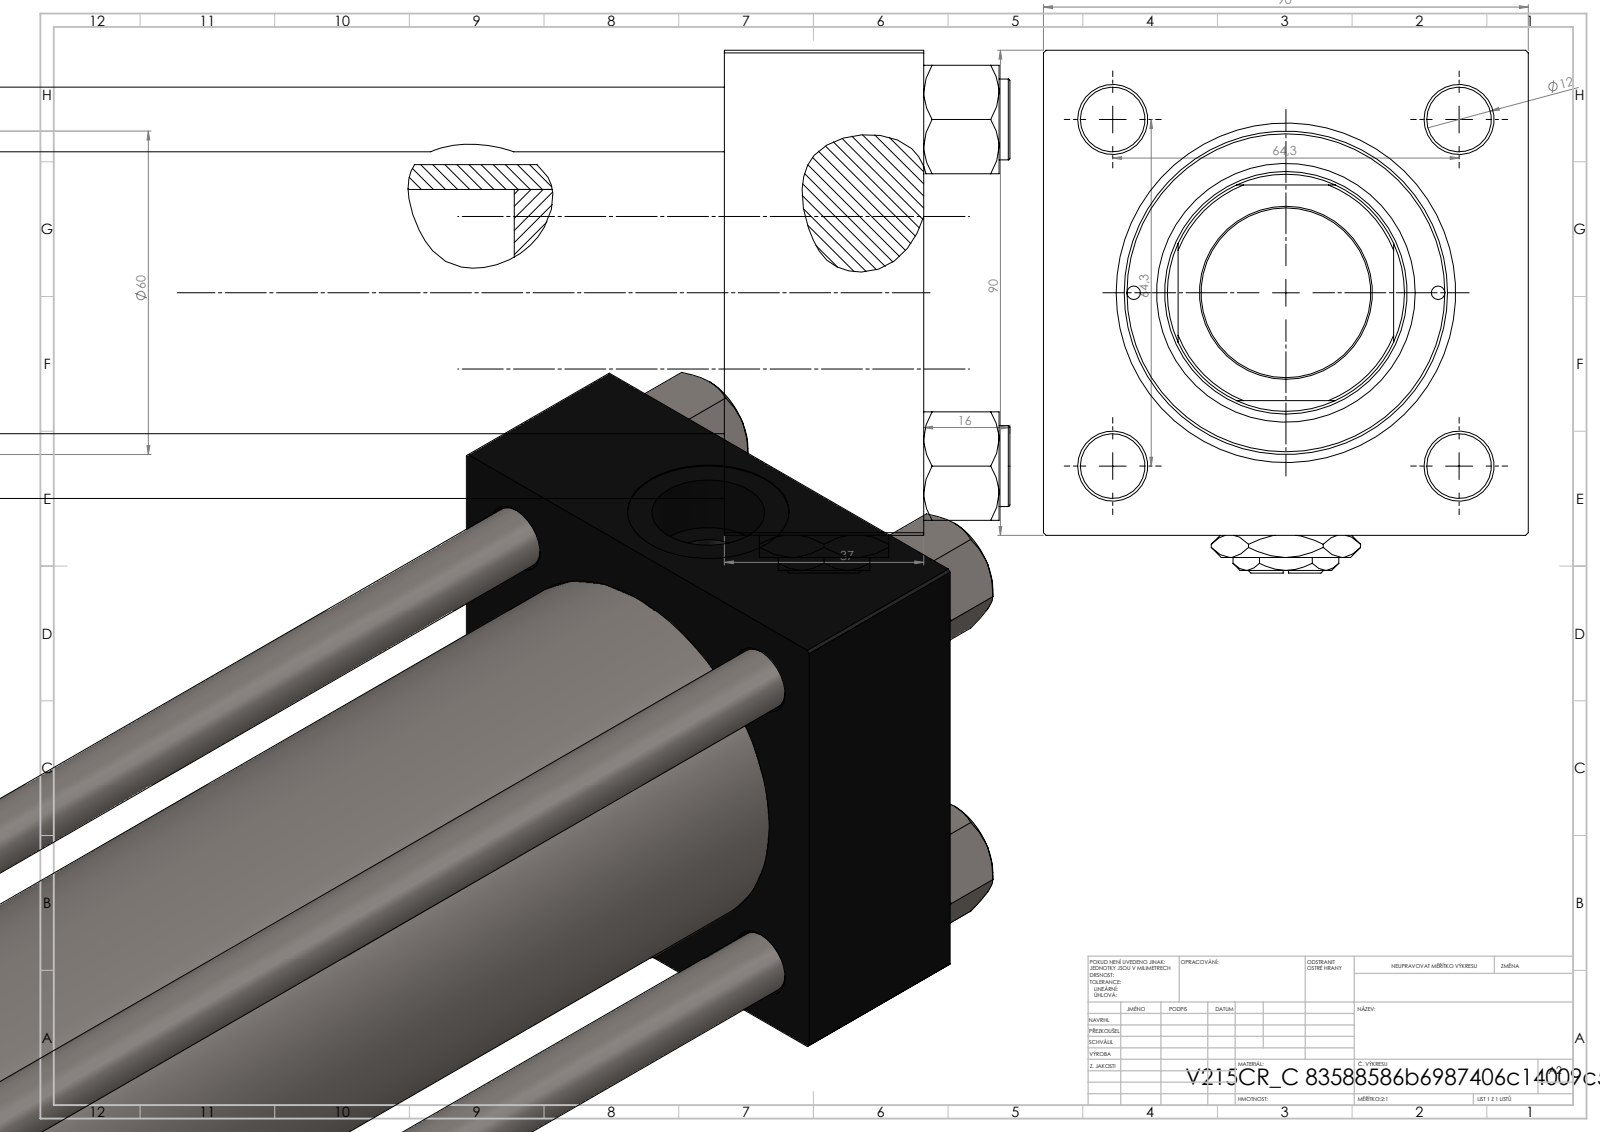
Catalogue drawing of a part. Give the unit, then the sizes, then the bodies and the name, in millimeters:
Units: millimetres
Overall size (bounding box): 533 × 97 × 90
Round holes (diameter × count): ⌀12 ×4, ⌀2.5 ×2, ⌀7 ×2, ⌀20.96 ×2, ⌀30 ×2, ⌀31.5 ×1, ⌀45 ×1, ⌀48 ×1, ⌀50 ×1, ⌀60 ×1, ⌀63 ×1
Round bosses / shafts (diameter × count): ⌀15 ×4, ⌀69 ×1
Partial cylindrical surfaces — rounded edges, fillets, slot ends (radius × count): R22 ×1
Main face-to-face distances: 90, 37, 59, 426, 389, 448, 485, 89.8, 456.3, 419.3
Hole centre spacings: 32.39, 45.47, 64.3, 68.42, 28.25, 90.93, 56.5, 427.5
Volume: 1 870 000 mm³ · Surface area: 428 379 mm²
Bodies: 13 solids, 1253 faces (575 planar, 100 cylindrical, 578 other)
Part name (STEP PRODUCT): V215CR_VCP_C; NUT_M5_C; V215CR_C_Body; V215_VC_A (+2 more)
STEP written by: SolidWorks 2019 (CONFIG_CONTROL_DESIGN)
